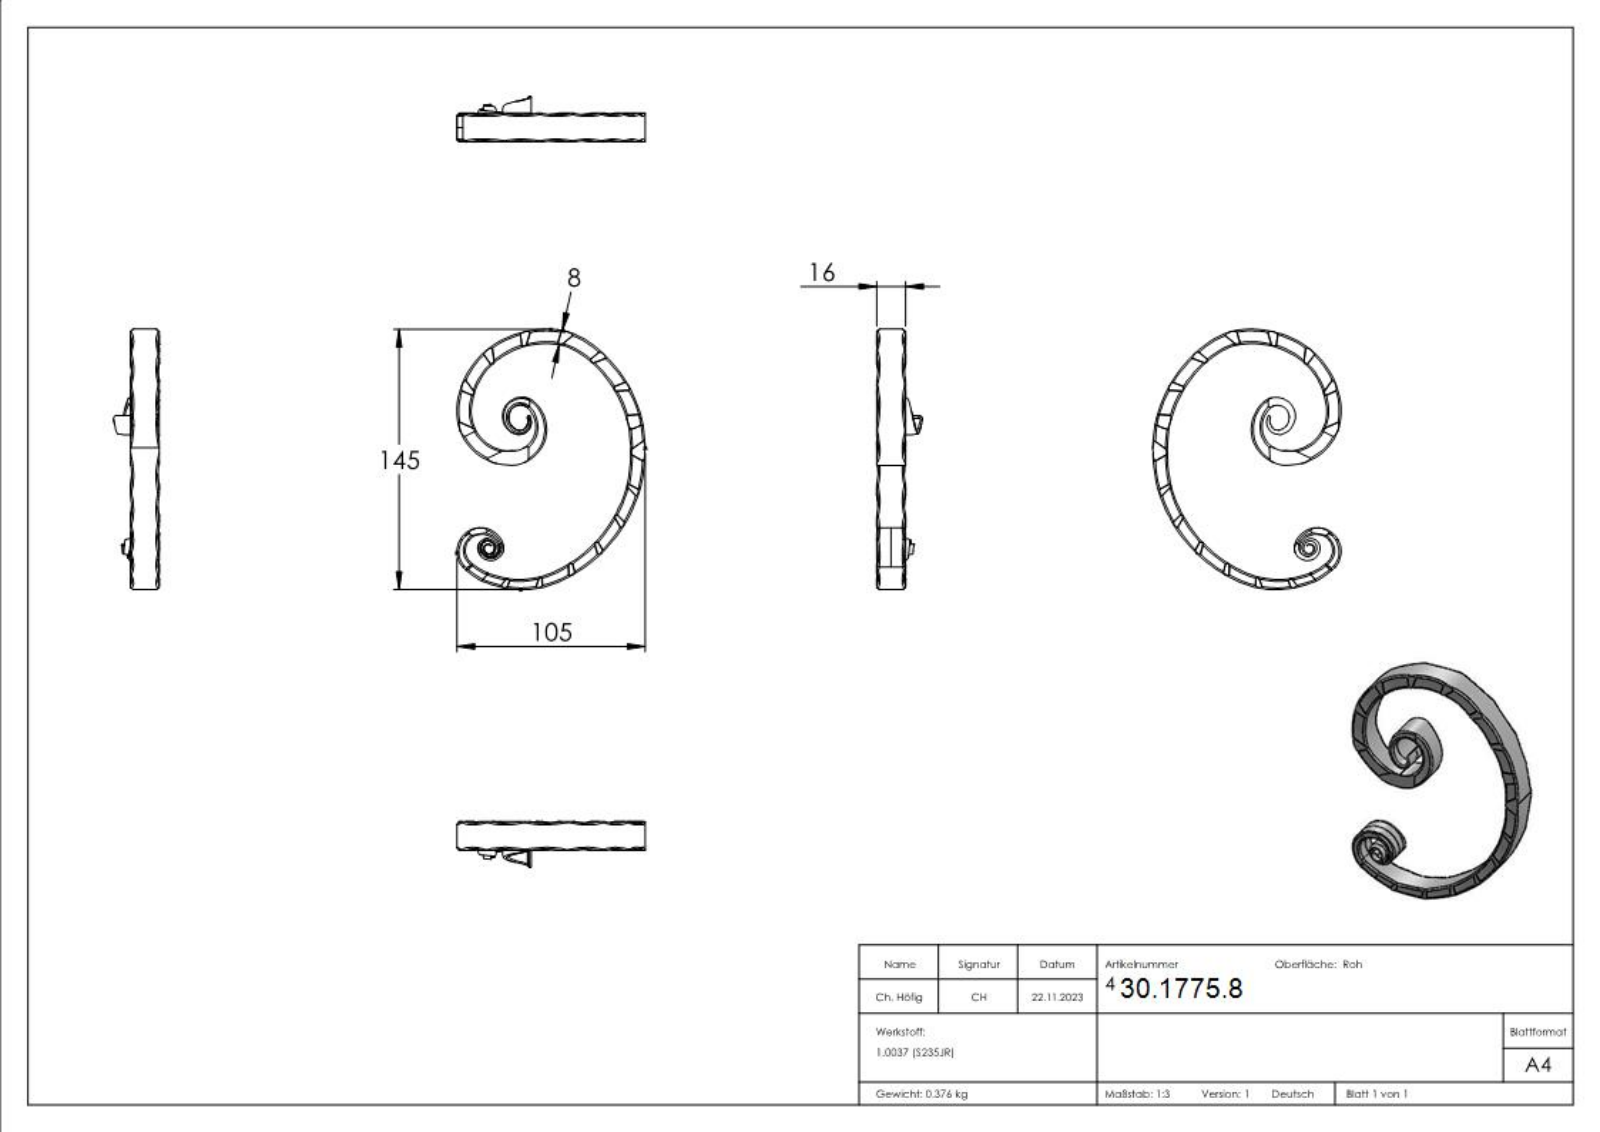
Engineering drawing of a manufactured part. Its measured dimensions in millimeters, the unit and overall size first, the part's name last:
Units: millimetres
Overall size (bounding box): 145.06 × 104.98 × 26.16
Partial cylindrical surfaces — rounded edges, fillets, slot ends (radius × count): R1 ×65, R37.88 ×22, R17.61 ×2
Main face-to-face distances: 16
Volume: 48 220 mm³ · Surface area: 22 145 mm²
Bodies: 1 solid, 295 faces (50 planar, 91 cylindrical, 154 other)
Part name (STEP PRODUCT): 4515
STEP written by: SolidWorks 2015 (CONFIG_CONTROL_DESIGN)
